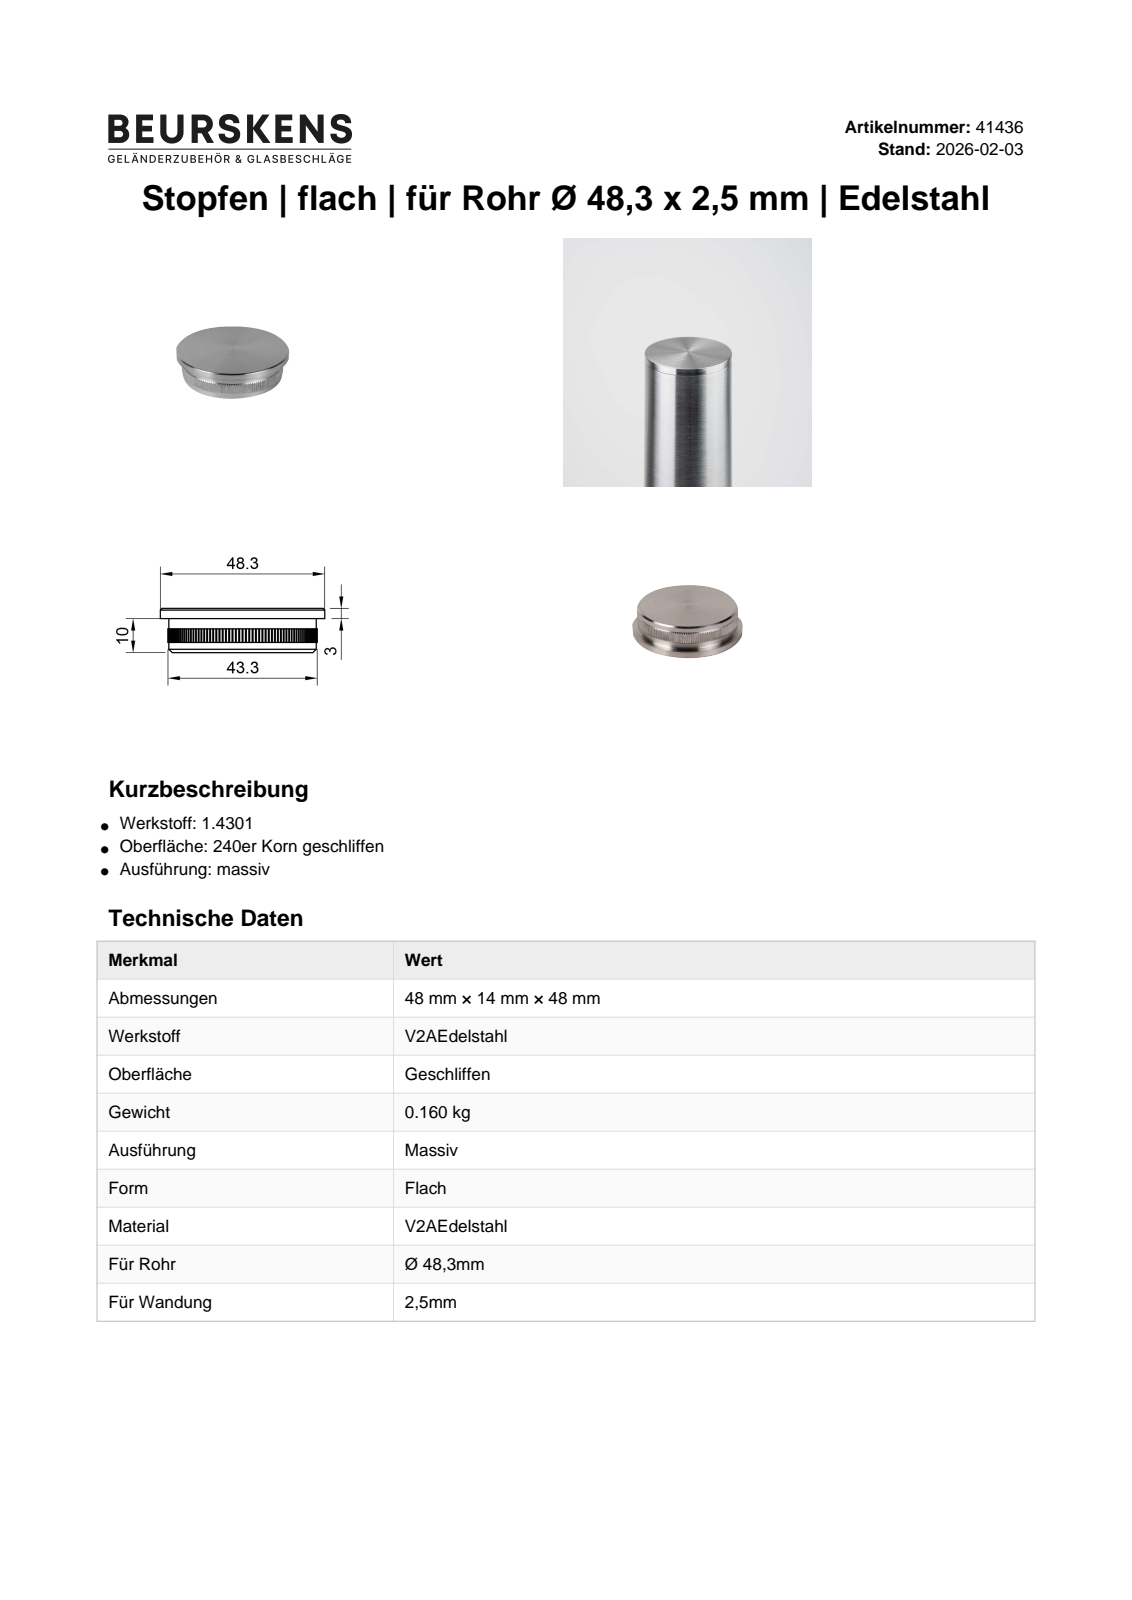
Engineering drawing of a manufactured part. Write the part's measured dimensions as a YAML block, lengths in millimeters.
part_name: "41436"
step_written_by: "Autodesk Inventor 2022 (AUTOMOTIVE_DESIGN)"
units: millimeters
bodies: {solids: 1, faces: 290, planar: 5, cylindrical: 283, other: 2}
overall_size: [48.3, 48.3, 13]
volume: 20287
surface_area: 5517
round_bosses_or_shafts:
  - {diameter: 48.3, count: 1}
  - {diameter: 43.3, count: 1}
partial_cylinders:
  - {radius: 0.12, count: 140}
  - {radius: 21.95, count: 1}
face_to_face_distances: [13, 3, 10, 7, 4, 6]
